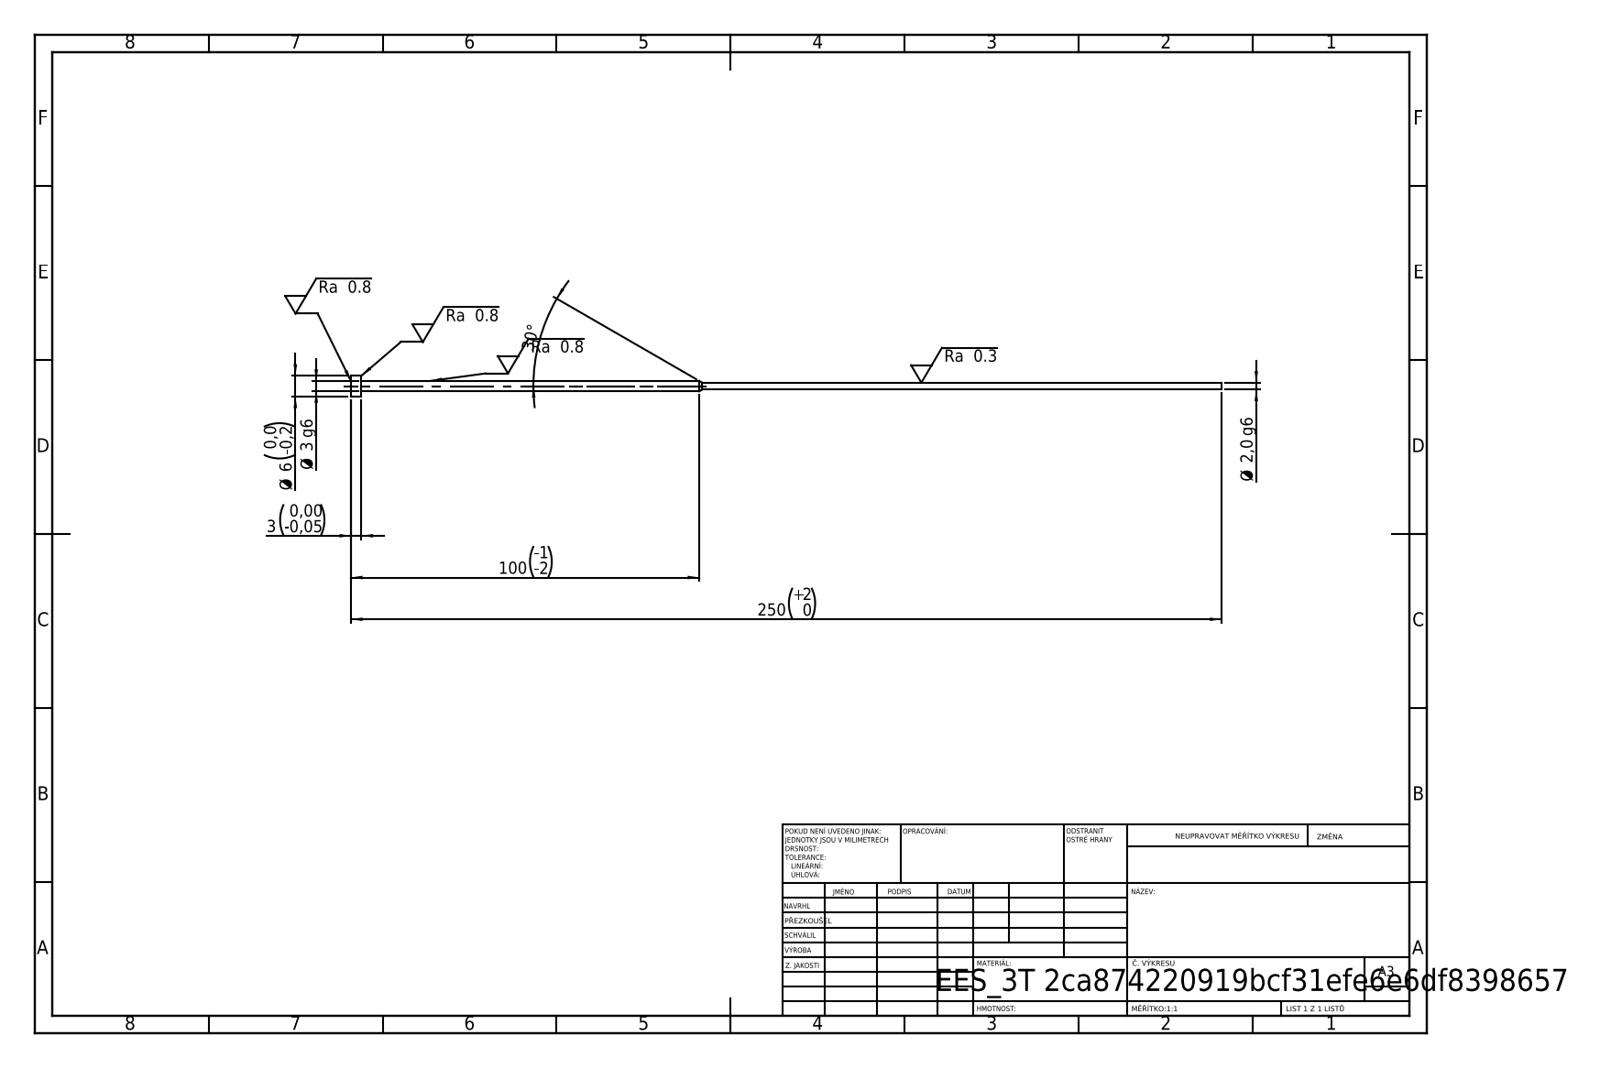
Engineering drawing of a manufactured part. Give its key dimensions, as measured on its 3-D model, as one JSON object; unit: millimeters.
{"step_written_by": "SolidWorks 2019 (CONFIG_CONTROL_DESIGN)", "units": "millimeters", "bodies": {"solids": 1, "faces": 11, "planar": 3, "cylindrical": 6, "other": 2}, "overall_size": [250, 6, 6], "volume_mm3": 1243, "surface_area_mm2": 1968, "round_bosses_or_shafts": [[6, 1], [3, 1], [2, 1]], "face_to_face_distances": [3, 247, 250]}
